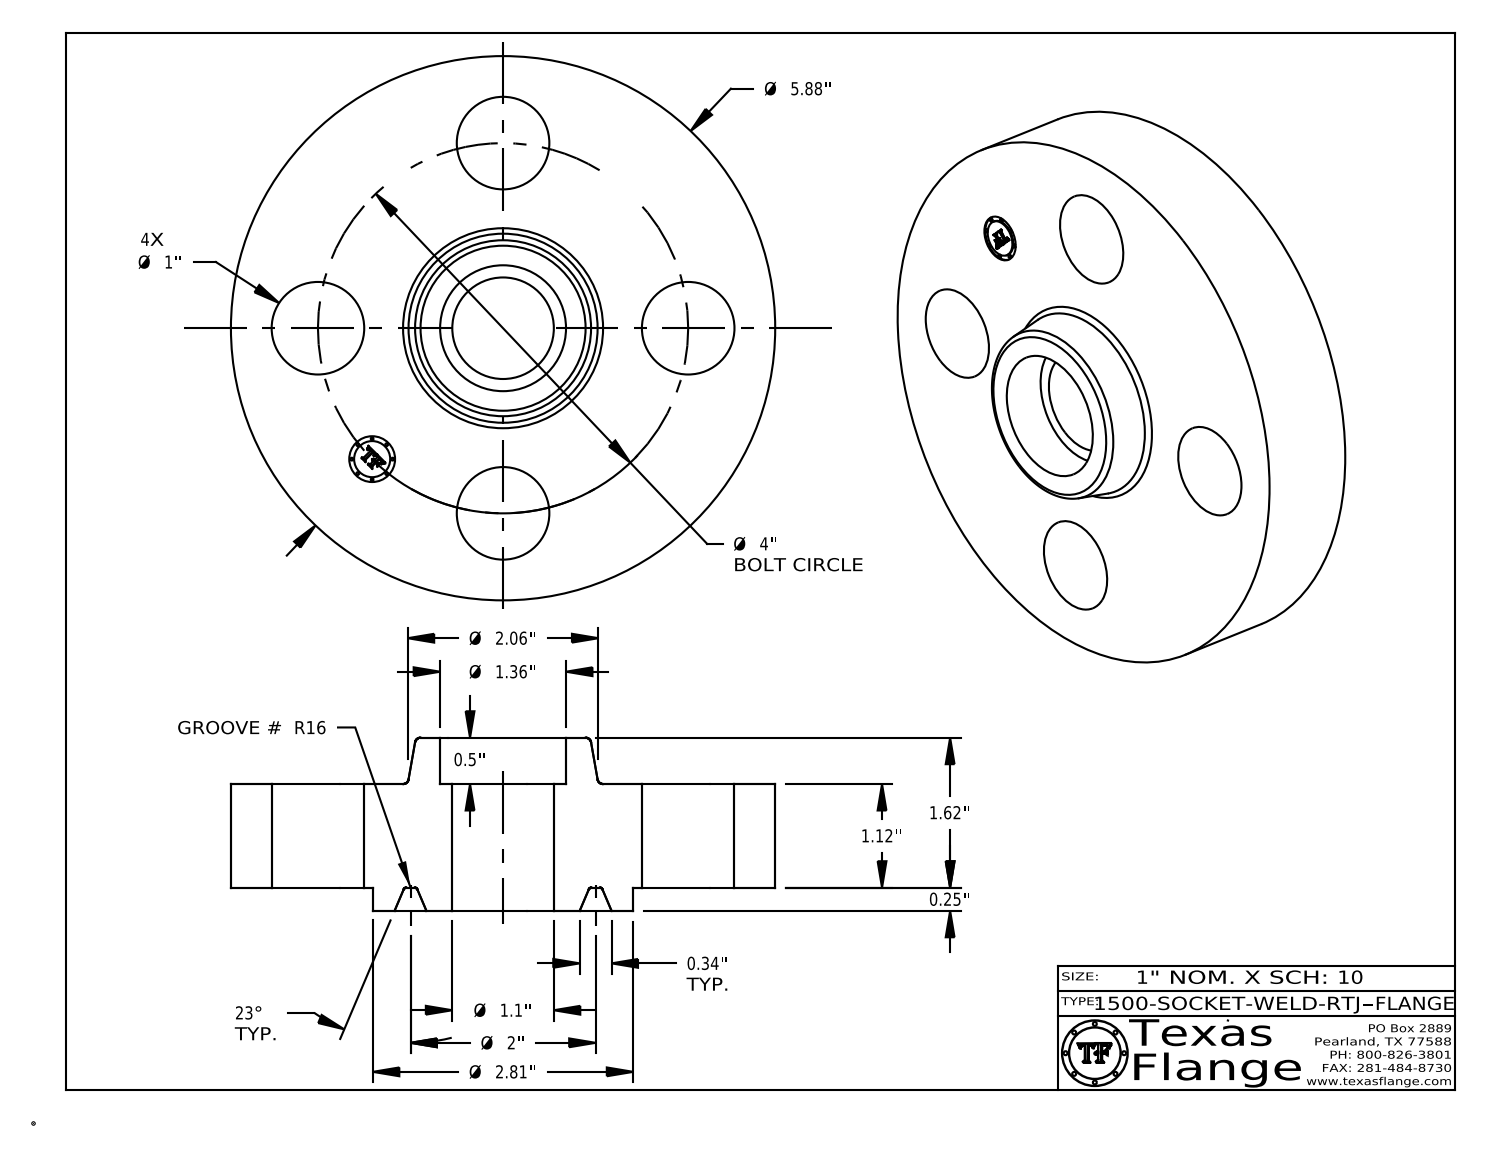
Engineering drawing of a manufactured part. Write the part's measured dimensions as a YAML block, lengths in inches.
part_name: "1500-SOCKET-WELD-RTJ"
step_written_by: "CATIA V5 STEP AP214 (AUTOMOTIVE_DESIGN)"
units: inches
bodies: {solids: 1, faces: 422, planar: 372, cylindrical: 36, other: 14}
overall_size: [5.88, 5.88, 1.87]
volume: 27.58
surface_area: 94.47
round_holes:
  - {diameter: 1, count: 4}
  - {diameter: 0.495, count: 1}
  - {diameter: 1.097, count: 1}
  - {diameter: 1.36, count: 1}
round_bosses_or_shafts:
  - {diameter: 0.03, count: 8}
  - {diameter: 5.88, count: 1}
  - {diameter: 2.813, count: 1}
  - {diameter: 0.39, count: 1}
face_to_face_distances: [1.12, 0.25, 1.37, 1.87, 1.62, 0.5, 0.015, 1.355, 1.105, 0.515]
hole_center_spacings: [2, 2.828, 1.531, 3.695, 4]
